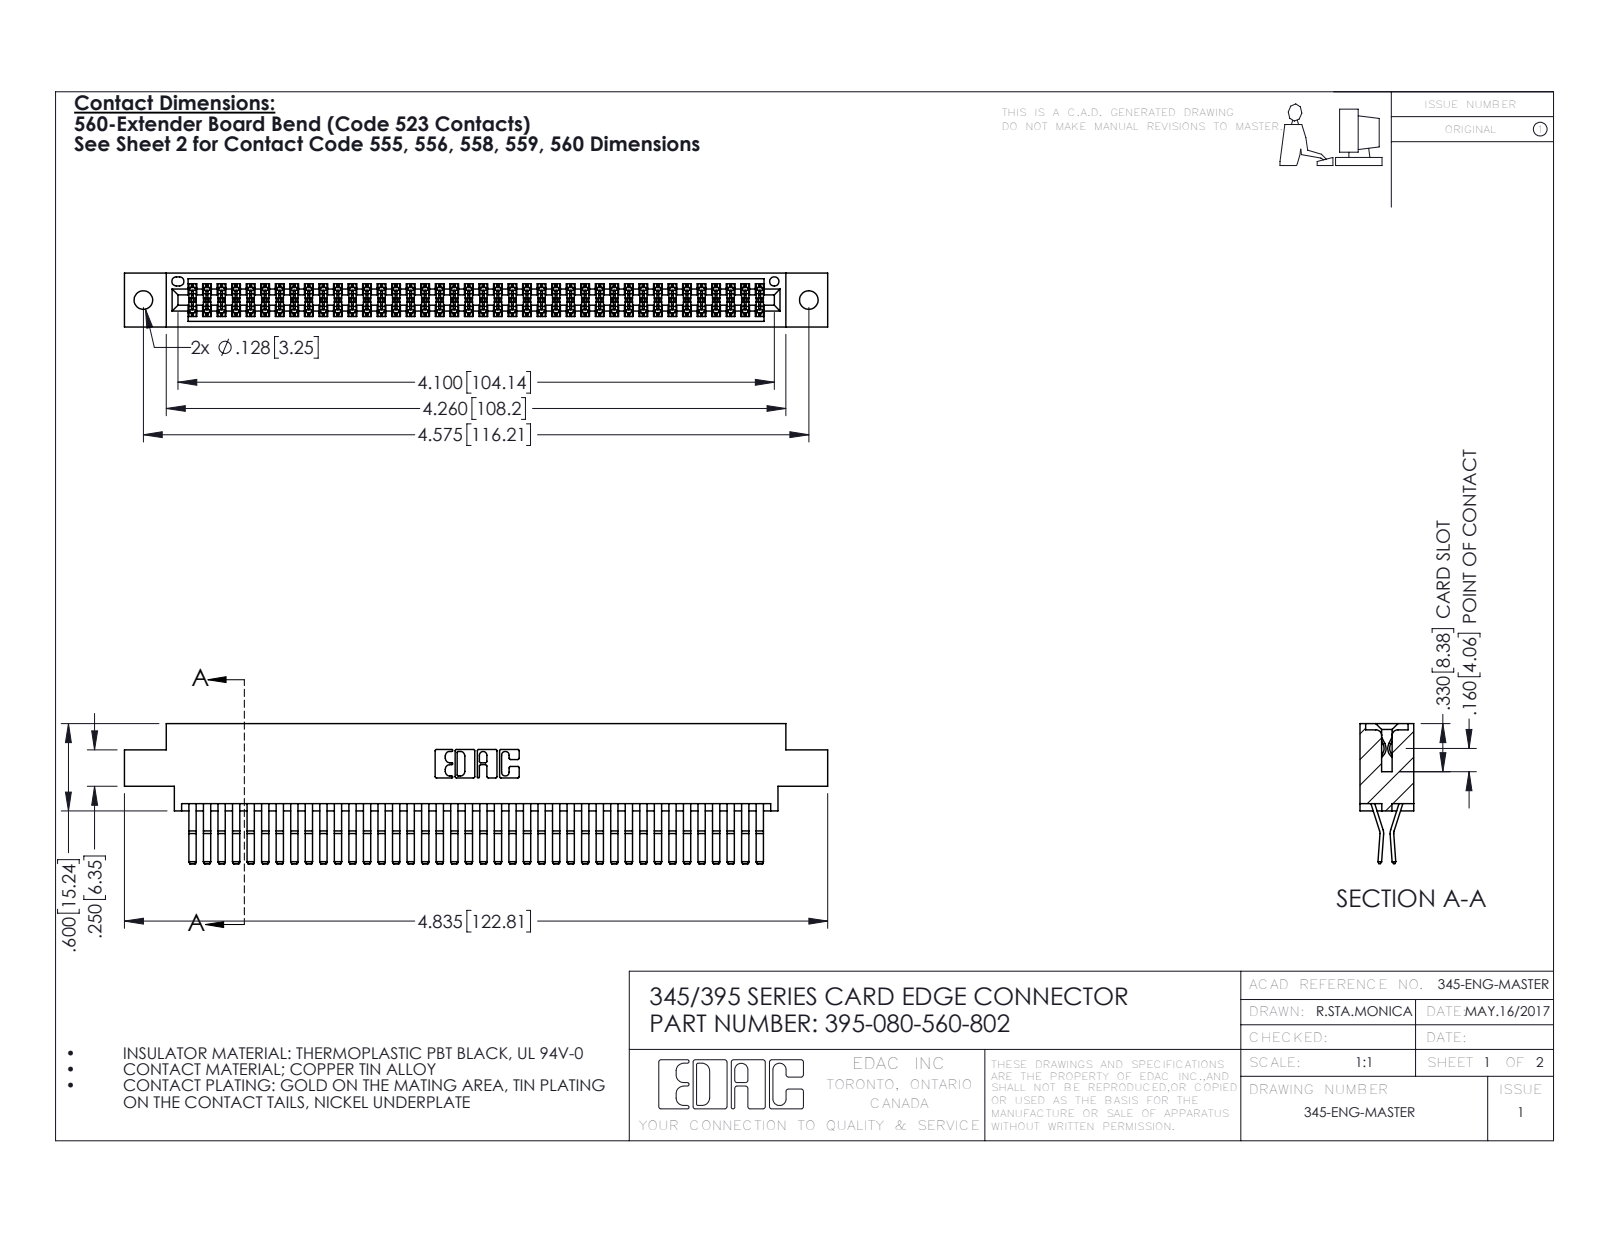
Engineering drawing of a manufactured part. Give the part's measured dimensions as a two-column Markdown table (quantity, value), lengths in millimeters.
| quantity | value |
| --- | --- |
| part name | 345 Part_0.170 Offset - 0.128 Dia; 395-080-560-802; 345-292-001_560 Tail |
| STEP written by | SolidWorks 2016 (CONFIG_CONTROL_DESIGN) |
| units | millimeters |
| bodies | 81 solids, 4290 faces (2724 planar, 1566 cylindrical, 0 other) |
| overall size | 122.8 × 24.4 × 9.4 |
| volume | 12 300 mm³ |
| surface area | 19 340 mm² |
| round holes (diameter × count) | 3.3 × 2, 1.6 × 1 |
| partial cylindrical surfaces (radius × count) | 0.2 × 120, 0.3 × 22, 0.2 × 6, 0.8 × 6, 0.7 × 3, 0.3 × 2, 0.4 × 2, 0.5 × 2 |
| main face-to-face distances | 0.6, 7.6, 1.8, 9.4, 5.1, 2.5, 6.9, 5.7, 4.4, 3.8 |
| hole center spacings | 6.9, 110.2, 116.2 |
